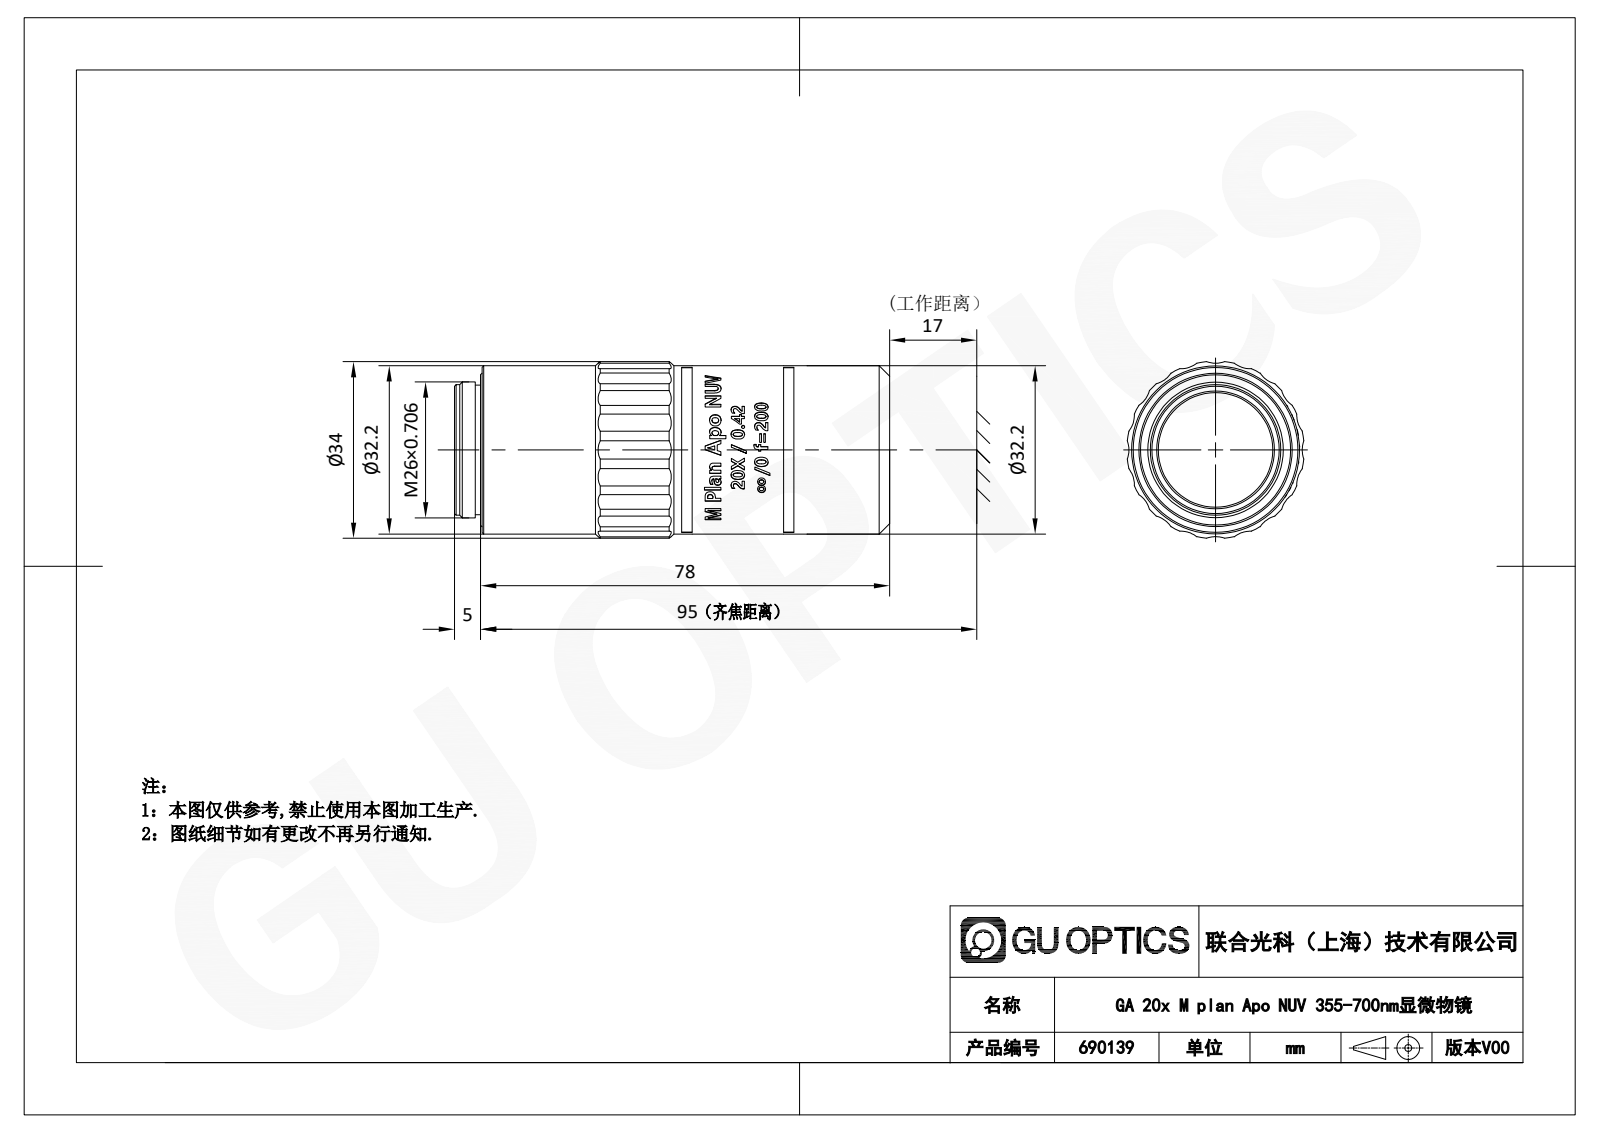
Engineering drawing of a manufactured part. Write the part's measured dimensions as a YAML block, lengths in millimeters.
part_name: "690139"
step_written_by: "SolidWorks 2020 (CONFIG_CONTROL_DESIGN)"
units: millimeters
bodies: {solids: 1, faces: 445, planar: 151, cylindrical: 101, other: 193}
overall_size: [83.3, 33.82, 33.82]
volume: 65011
surface_area: 10447
round_holes:
  - {diameter: 22, count: 1}
  - {diameter: 24, count: 1}
round_bosses_or_shafts:
  - {diameter: 32.2, count: 1}
  - {diameter: 32, count: 1}
  - {diameter: 26, count: 1}
  - {diameter: 25, count: 1}
  - {diameter: 24.8, count: 1}
partial_cylinders:
  - {radius: 5, count: 20}
  - {radius: 17, count: 1}
face_to_face_distances: [1.3, 79.6, 78.3, 1.6, 78, 5, 3.7, 5.3, 83.3, 4]
